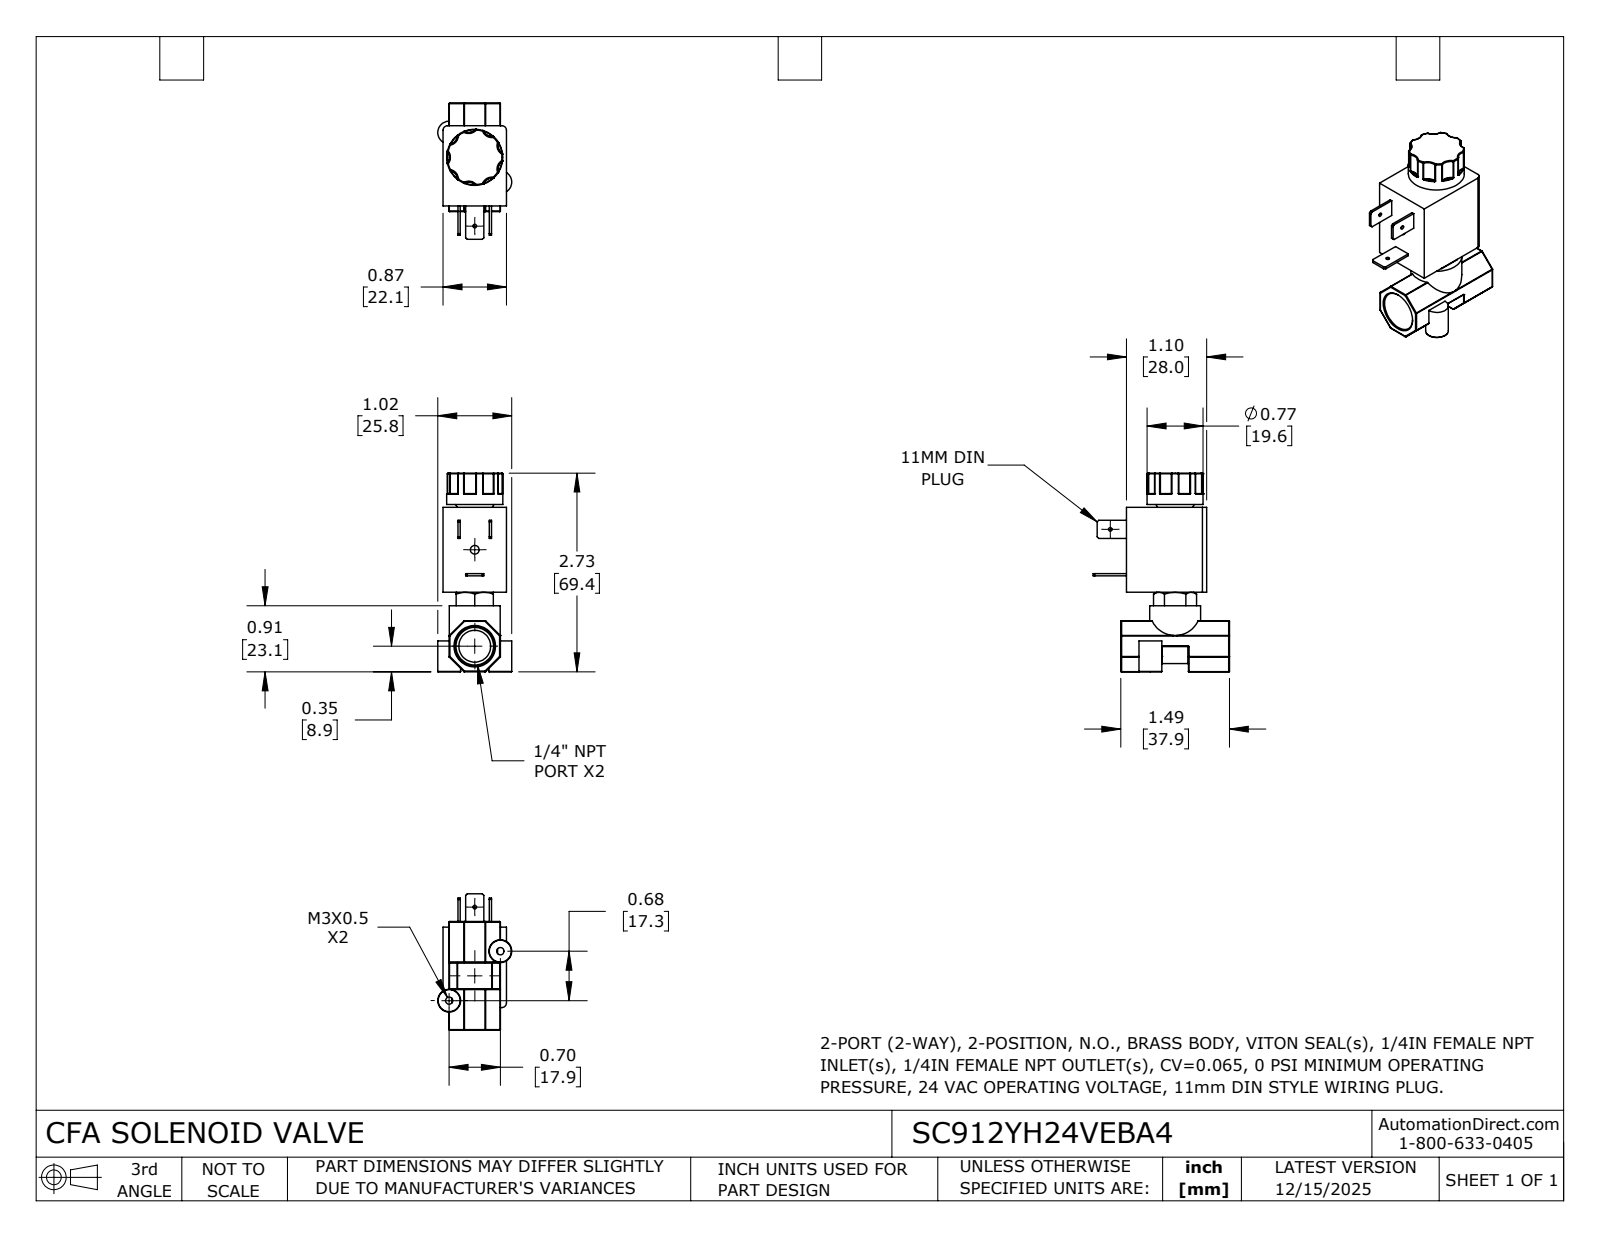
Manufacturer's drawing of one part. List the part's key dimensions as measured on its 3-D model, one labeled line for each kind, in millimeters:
Part name (STEP PRODUCT): SC912YH24VEBA4
STEP written by: SolidWorks 2024 (CONFIG_CONTROL_DESIGN)
Units: millimetres
Bodies: 1 solid, 350 faces (74 planar, 107 cylindrical, 169 other)
Overall size (bounding box): 69.4 × 47.6 × 25.8
Volume: 29 870 mm³ · Surface area: 10 510 mm²
Round holes (diameter × count): ⌀1.3 ×2, ⌀2.5 ×2, ⌀3 ×1, ⌀11.1 ×1
Round bosses / shafts (diameter × count): ⌀8 ×2, ⌀19.6 ×1, ⌀17.8 ×1
Partial cylindrical surfaces — rounded edges, fillets, slot ends (radius × count): R0.3 ×42, R0.1 ×14, R3.4 ×7, R1.5 ×2, R3.4 ×2, R6 ×1, R8 ×1
Main face-to-face distances: 22.1, 17.9, 28, 29.6, 2.1, 20, 27.8, 57.4, 69.4, 41.6
Hole centre spacings: 17.8, 24.9, 33.7, 33.9
